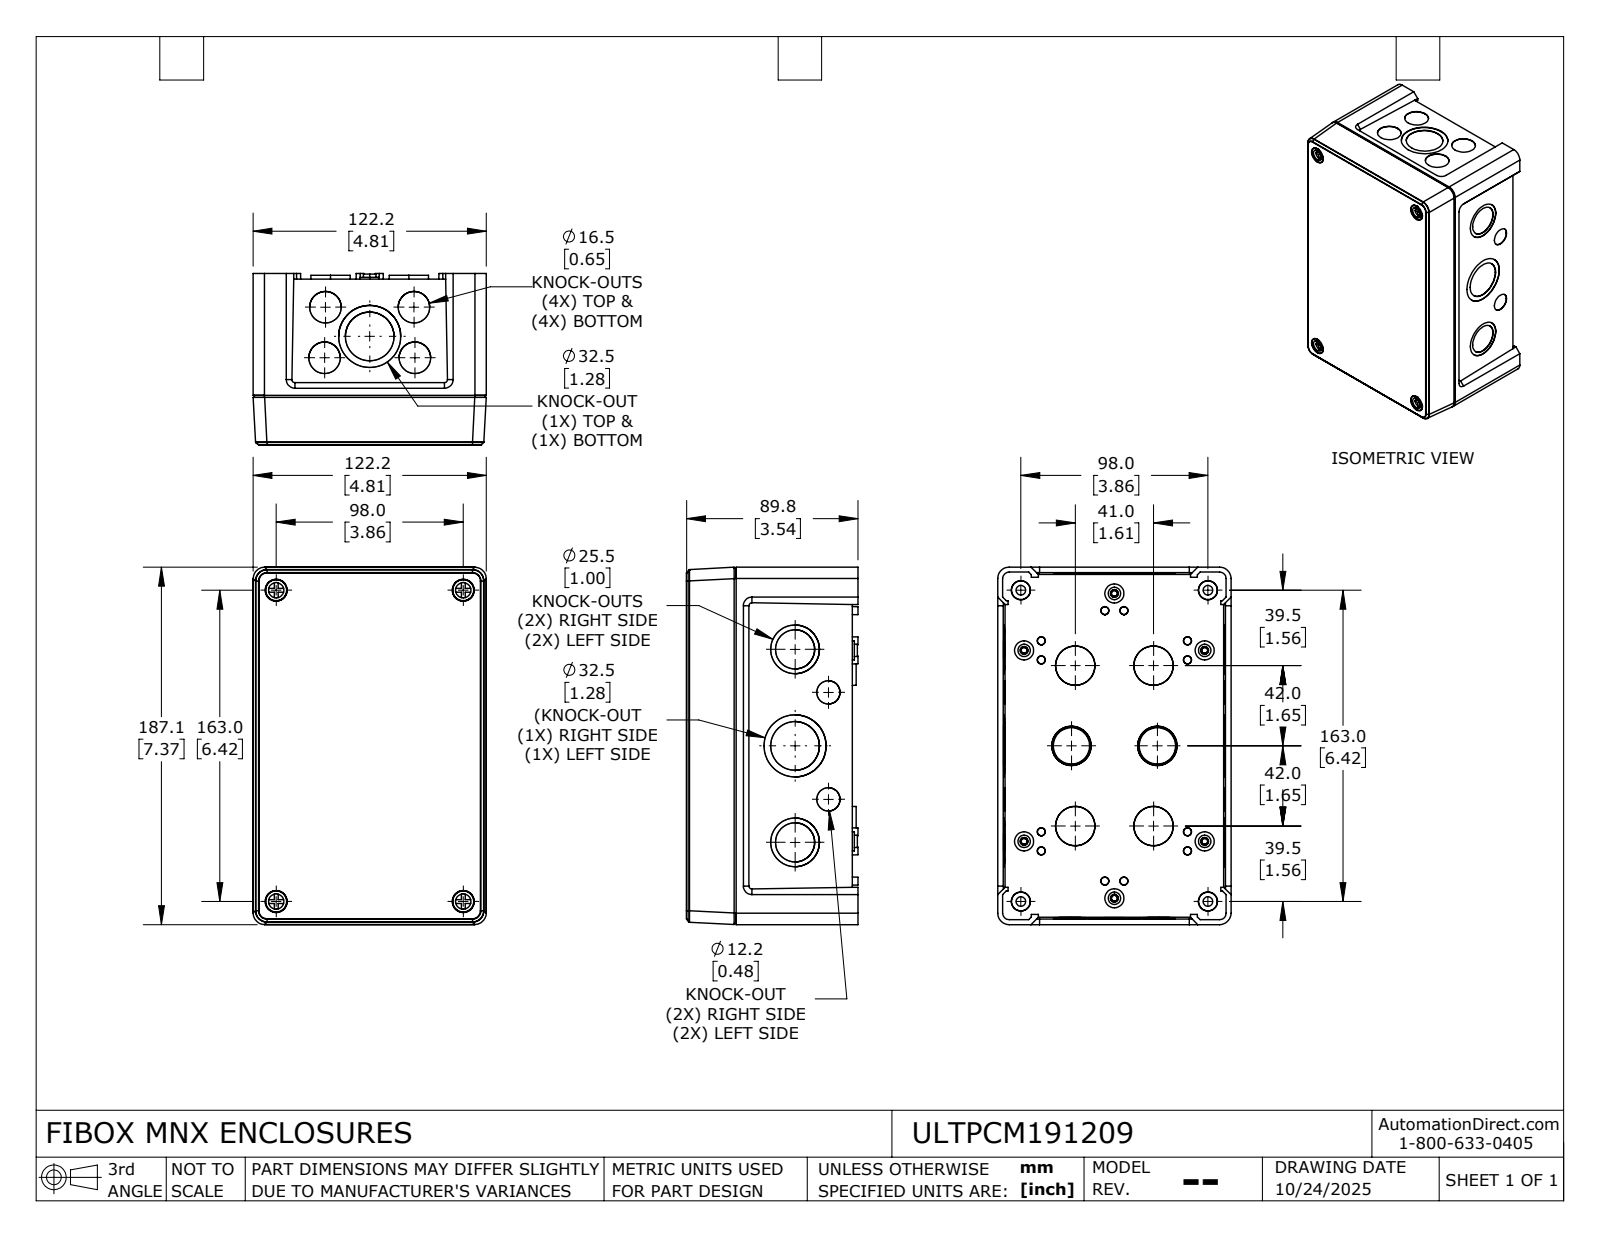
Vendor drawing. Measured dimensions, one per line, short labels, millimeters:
name: ULTPCM191209_Default
written by: SolidWorks 2024 (CONFIG_CONTROL_DESIGN)
unit: mm
bodies: 6 solids, 864 faces (406 planar, 160 cylindrical, 298 other)
size: 187.2 × 122.2 × 89.9
volume: 351 300 mm³; area: 214 800 mm²
holes: 8× ⌀16.5, 8× ⌀25.5, 4× ⌀5, 4× ⌀8, 4× ⌀12.2, 4× ⌀20.5, 4× ⌀32.5
bosses: 6× ⌀10, 6× ⌀6.5, 4× ⌀11, 4× ⌀7.2
rounds: 8× R0.3, 8× R0.5, 8× R1.5, 8× R6, 4× R3.4, 4× R5
face distances: 2.8, 84.1, 86.9, 2.3, 84.7, 2.2, 81.9, 3.3, 60.9, 58.7
hole spacings: 26.2, 26.5, 27.8, 28.5, 33, 50.5, 53.8, 80.4
